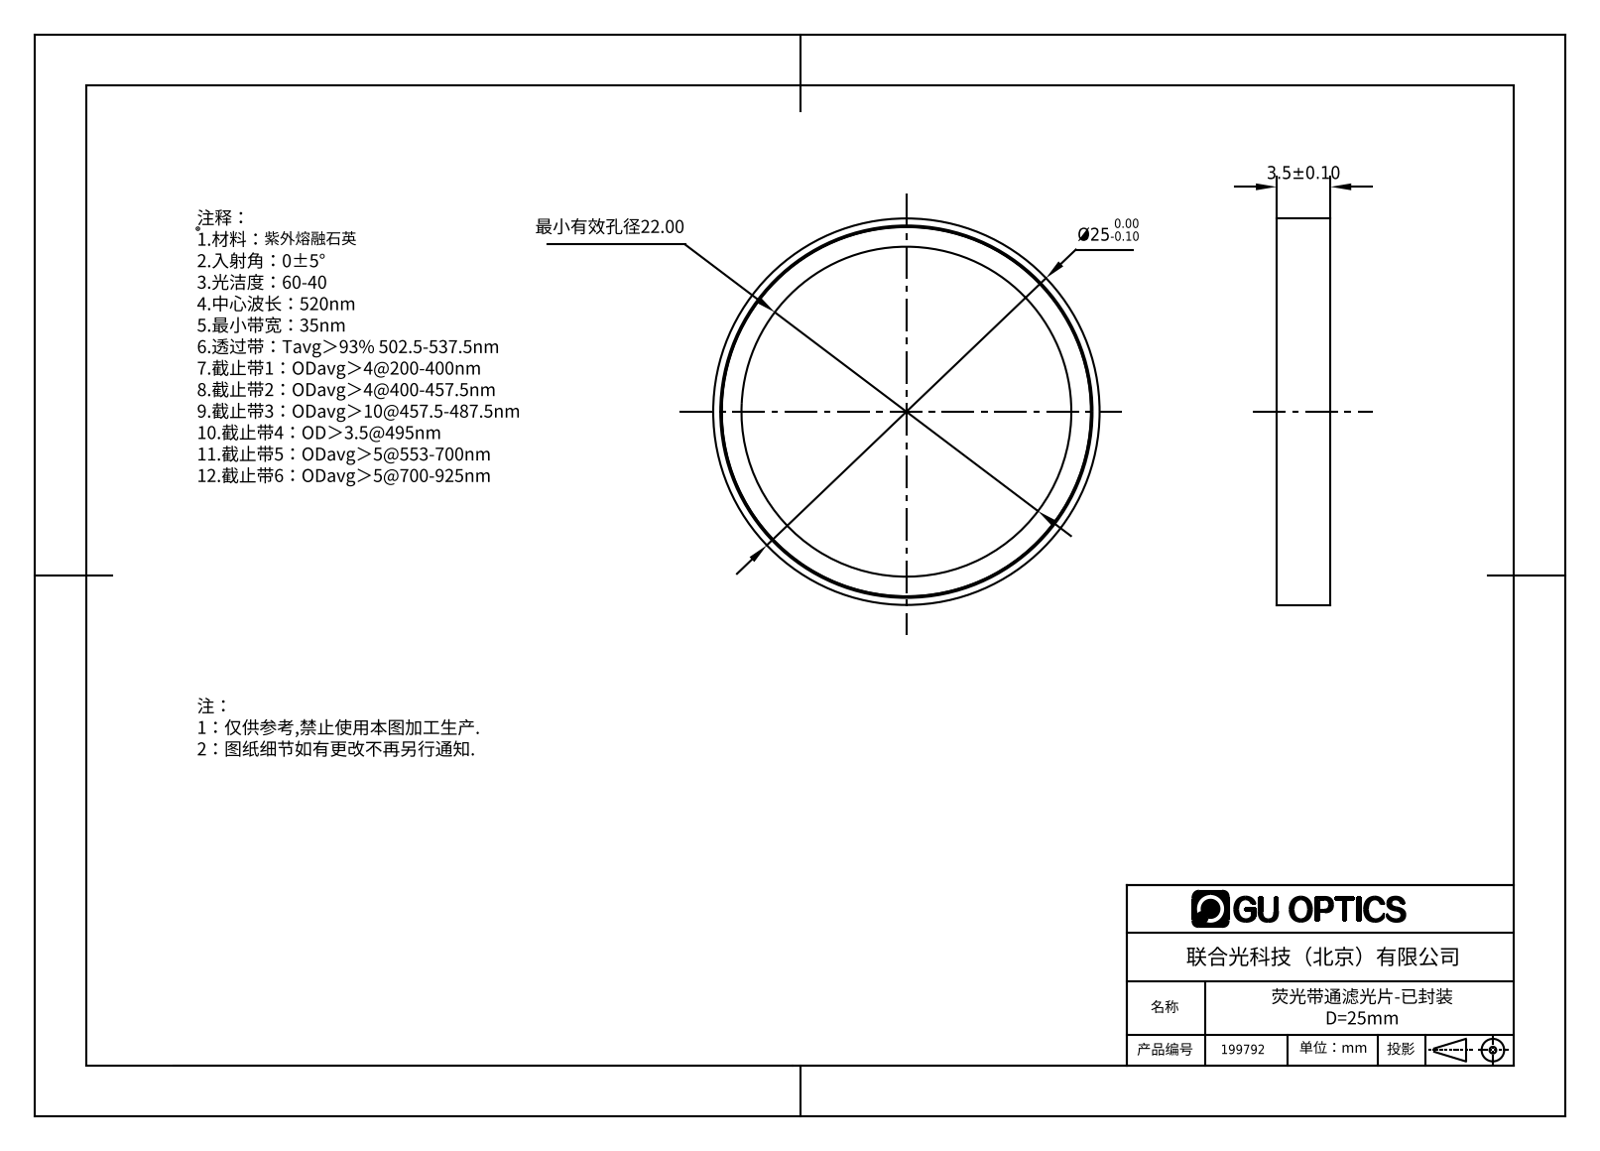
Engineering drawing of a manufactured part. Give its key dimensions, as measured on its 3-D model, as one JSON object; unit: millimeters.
{"part_name": "25mm 3.5mm 22mm", "step_written_by": "SolidWorks 2016 (AUTOMOTIVE_DESIGN)", "units": "millimeters", "bodies": {"solids": 3, "faces": 25, "planar": 9, "cylindrical": 16, "other": 0}, "overall_size": [24.99, 24.99, 3.5], "volume_mm3": 939, "surface_area_mm2": 2084, "round_holes": [[21.21, 1], [22, 1], [24.08, 1], [24.21, 1]], "round_bosses_or_shafts": [[24.99, 1], [23.9, 1], [23.88, 1]], "face_to_face_distances": [0.38, 1.62, 2, 2.38, 0.76, 2.76, 3.5, 3.12, 2.74, 1.12]}
